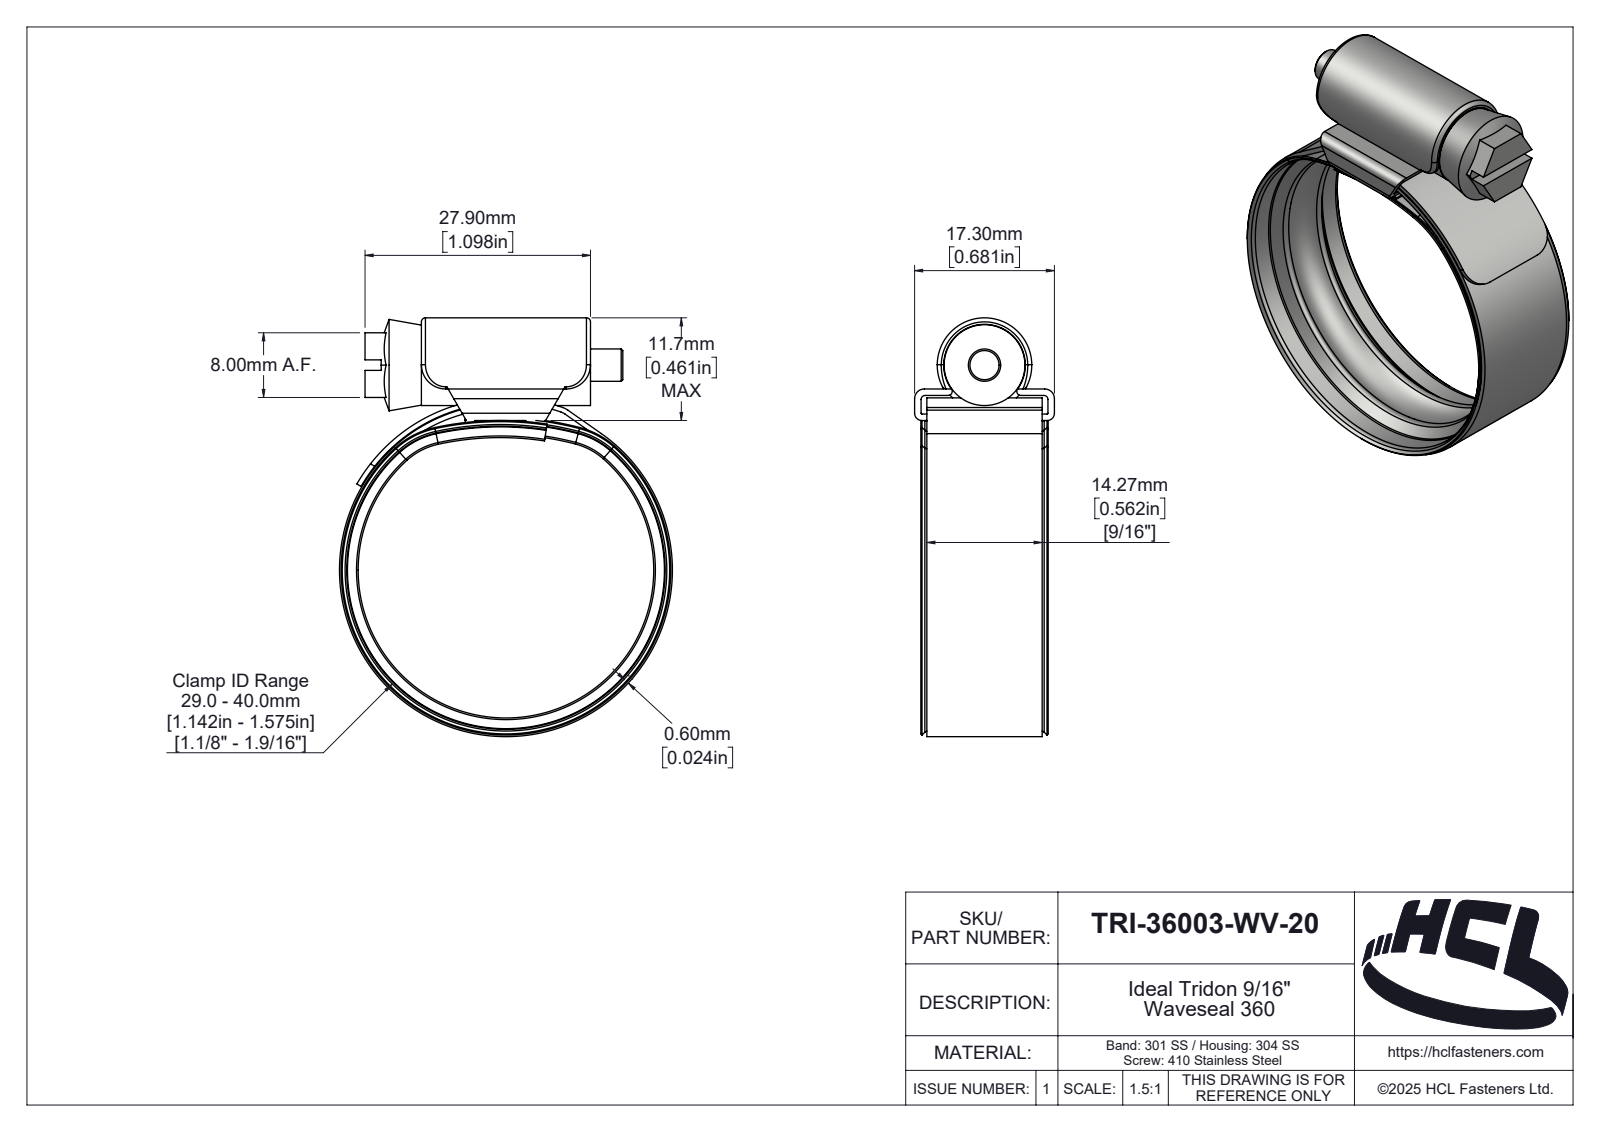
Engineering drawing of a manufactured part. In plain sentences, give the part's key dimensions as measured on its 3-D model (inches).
The part is named "TRI-36003-WV-20". Its 3-D file was written by "SolidWorks 2025 (AUTOMOTIVE_DESIGN)". It is 4 solids with 418 faces: 42 planar, 119 cylindrical and 257 other. Overall it measures 2.039 by 1.622 by 0.681 inches. Its volume is 0.28 cubic inches and its surface area 18.54 square inches. Round holes: 1 of diameter 1.575. Round bosses or shafts: 1 of diameter 1.622, 1 of diameter 0.394, 1 of diameter 0.157. Partial cylindrical surfaces (rounded edges, fillets, slot ends): 6 of radius 0.02, 4 of radius 0.118, 2 of radius 0.004, 2 of radius 0.035, 2 of radius 0.047, 2 of radius 0.39, 2 of radius 0.398, 1 of radius 0.018. The main face-to-face distances are 0.031, 0.122, 0.091, 0.561, 0.024, 0.154, 1.098, 0.06, 0.621, 0.65.
